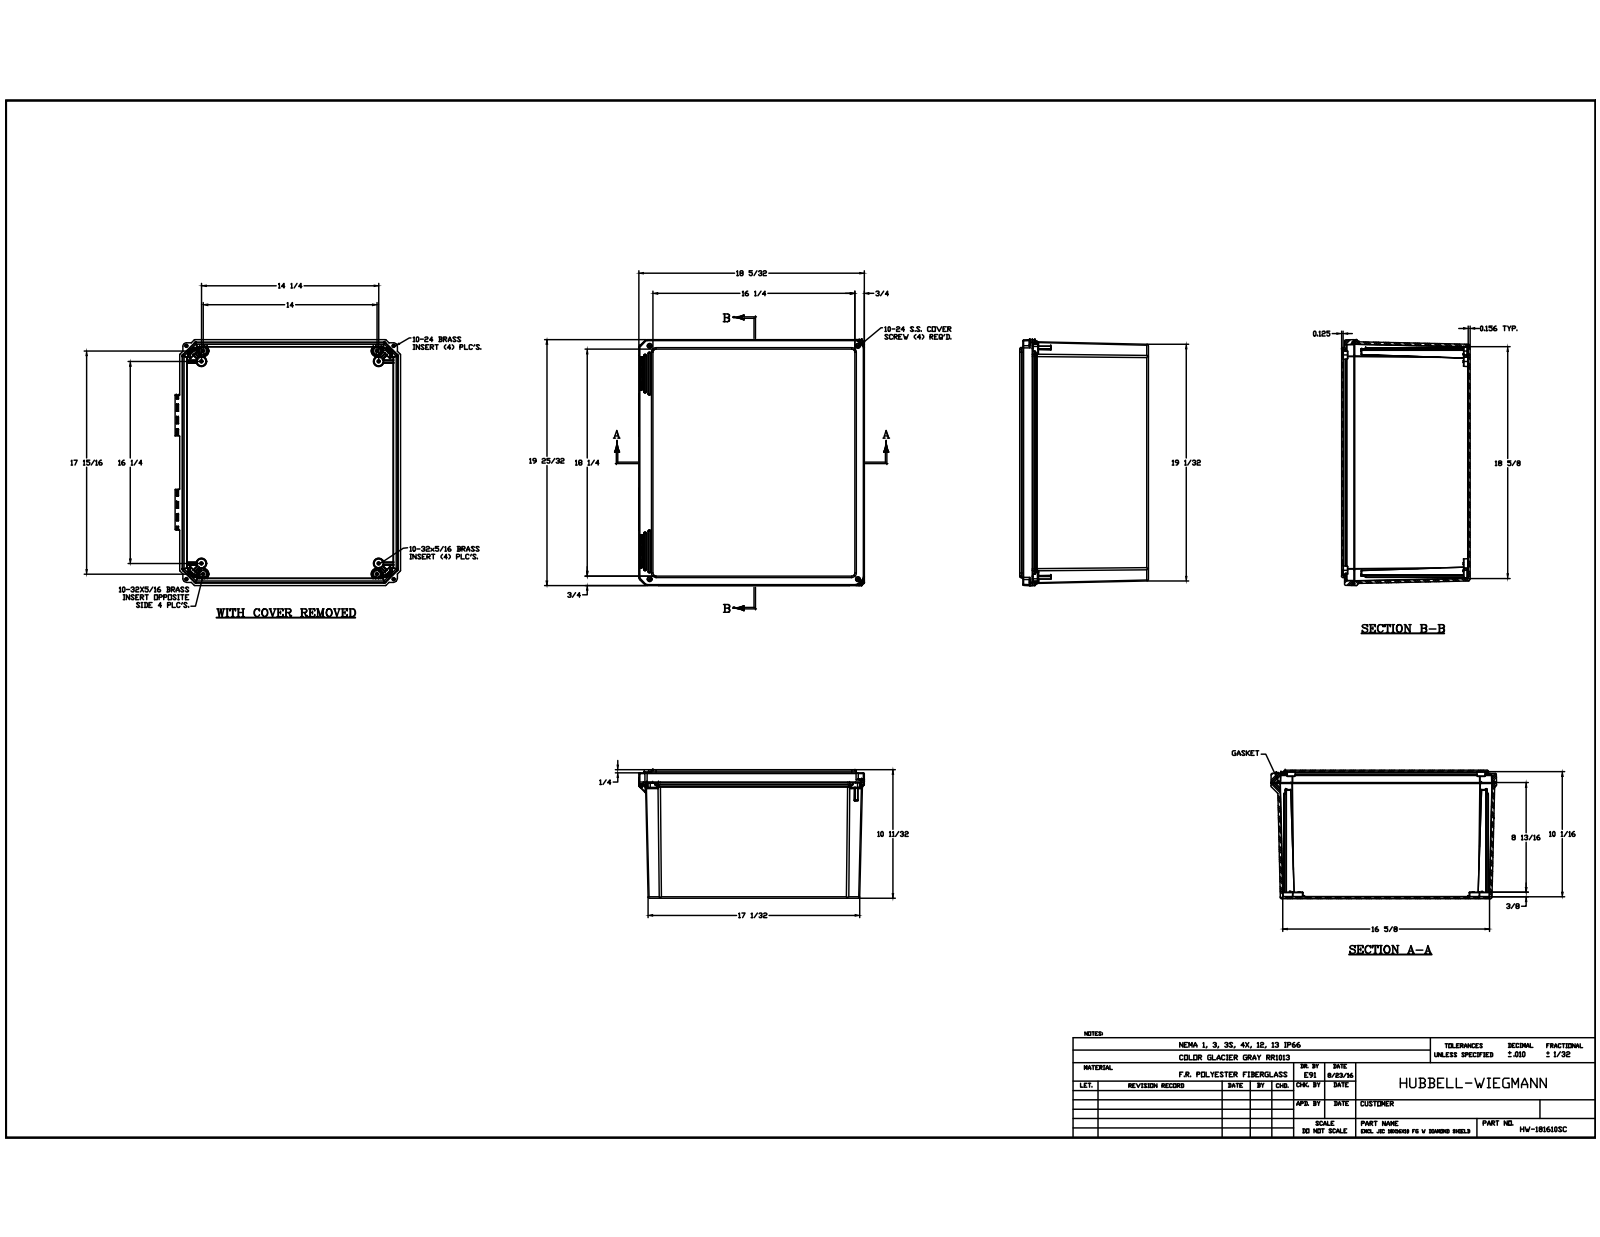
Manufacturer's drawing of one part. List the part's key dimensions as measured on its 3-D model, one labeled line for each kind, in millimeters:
Part name (STEP PRODUCT): HW-181610SC; DS181610BOX; DS181610CVR; BRASS INSERT-(_1 (+6 more)
STEP written by: Autodesk Inventor 2017 (CONFIG_CONTROL_DESIGN)
Units: millimetres
Bodies: 27 solids, 2174 faces (746 planar, 786 cylindrical, 642 other)
Overall size (bounding box): 502.62 × 460.94 × 262.67
Volume: 4 244 000 mm³ · Surface area: 1 899 000 mm²
Round holes (diameter × count): ⌀3.96 ×16, ⌀3.86 ×8, ⌀6.4 ×4, ⌀6.43 ×4, ⌀5.56 ×2, ⌀5.77 ×2, ⌀7.94 ×2, ⌀3.48 ×1
Round bosses / shafts (diameter × count): ⌀6.25 ×16, ⌀11.43 ×4, ⌀5.05 ×4, ⌀11.05 ×2
Partial cylindrical surfaces — rounded edges, fillets, slot ends (radius × count): R0.25 ×170, R0.13 ×88, R0.51 ×49, R0.76 ×42, R1.59 ×26, R0.76 ×24, R2.29 ×24, R2.44 ×24
Main face-to-face distances: 3.17, 3.96, 258.71, 262.67, 5.13, 5.08, 259.5, 255.54, 6.35, 3.18
Hole centre spacings: 594.16, 21.74, 359.42, 395.28, 434.28, 445.91, 390.94, 426.01
